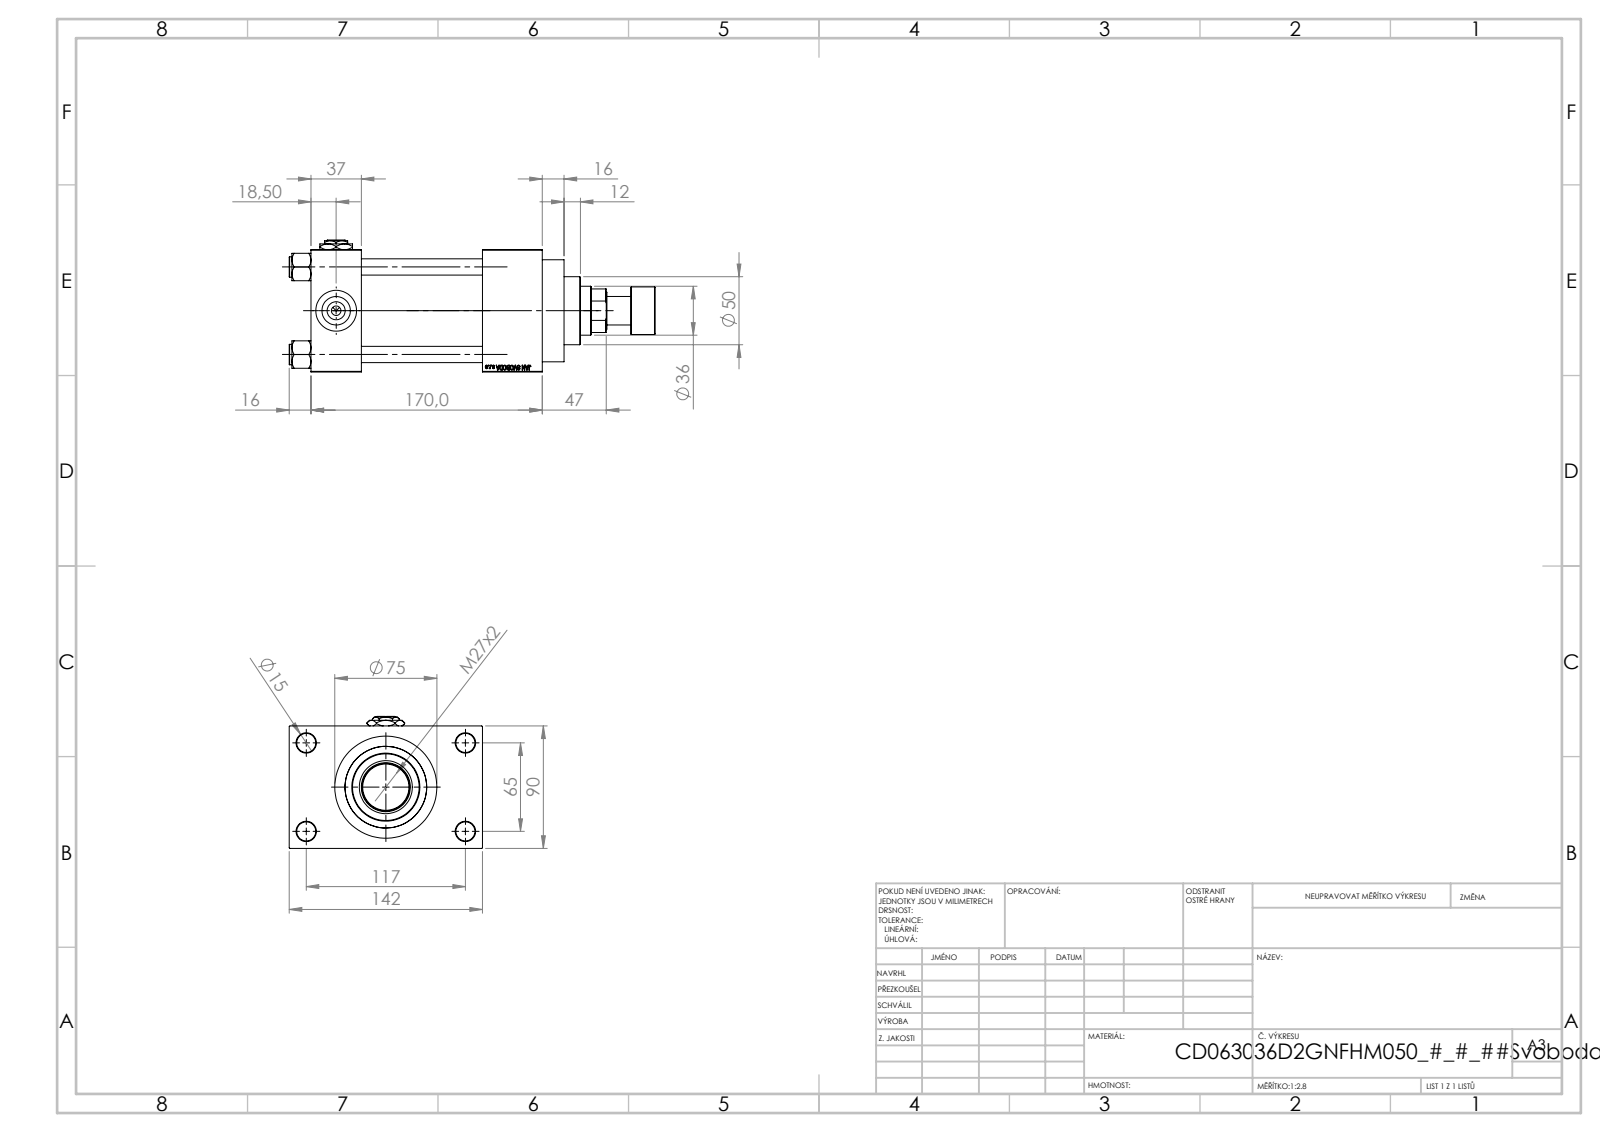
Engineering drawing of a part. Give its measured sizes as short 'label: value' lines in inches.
name: Zatka_pro_OIL_PORT; V215CD_D_Body; V215CD_VCP_D; V215CD_VC_A (+3 more)
written by: SolidWorks 2019 (CONFIG_CONTROL_DESIGN)
unit: in
bodies: 13 solids, 1170 faces (525 planar, 99 cylindrical, 546 other)
size: 10.591 × 5.591 × 3.819
volume: 72.98 in³; area: 363.4 in²
holes: 4× ⌀0.472, 4× ⌀0.551, 3× ⌀0.276, 3× ⌀0.825, 3× ⌀1.181, 1× ⌀1.004, 1× ⌀1.417, 1× ⌀1.535, 1× ⌀1.969, 1× ⌀2.362, 1× ⌀2.48
bosses: 4× ⌀0.591, 1× ⌀2.953, 1× ⌀2.717, 1× ⌀1.378, 1× ⌀0.827
face distances: 3.543, 3.504, 1.457, 4.961, 6.693, 5.236, 1.732, 4.567, 1.024, 5.591
hole spacings: 1.037, 1.79, 2.531, 2.635, 2.748, 3.569, 4.383, 2.559
